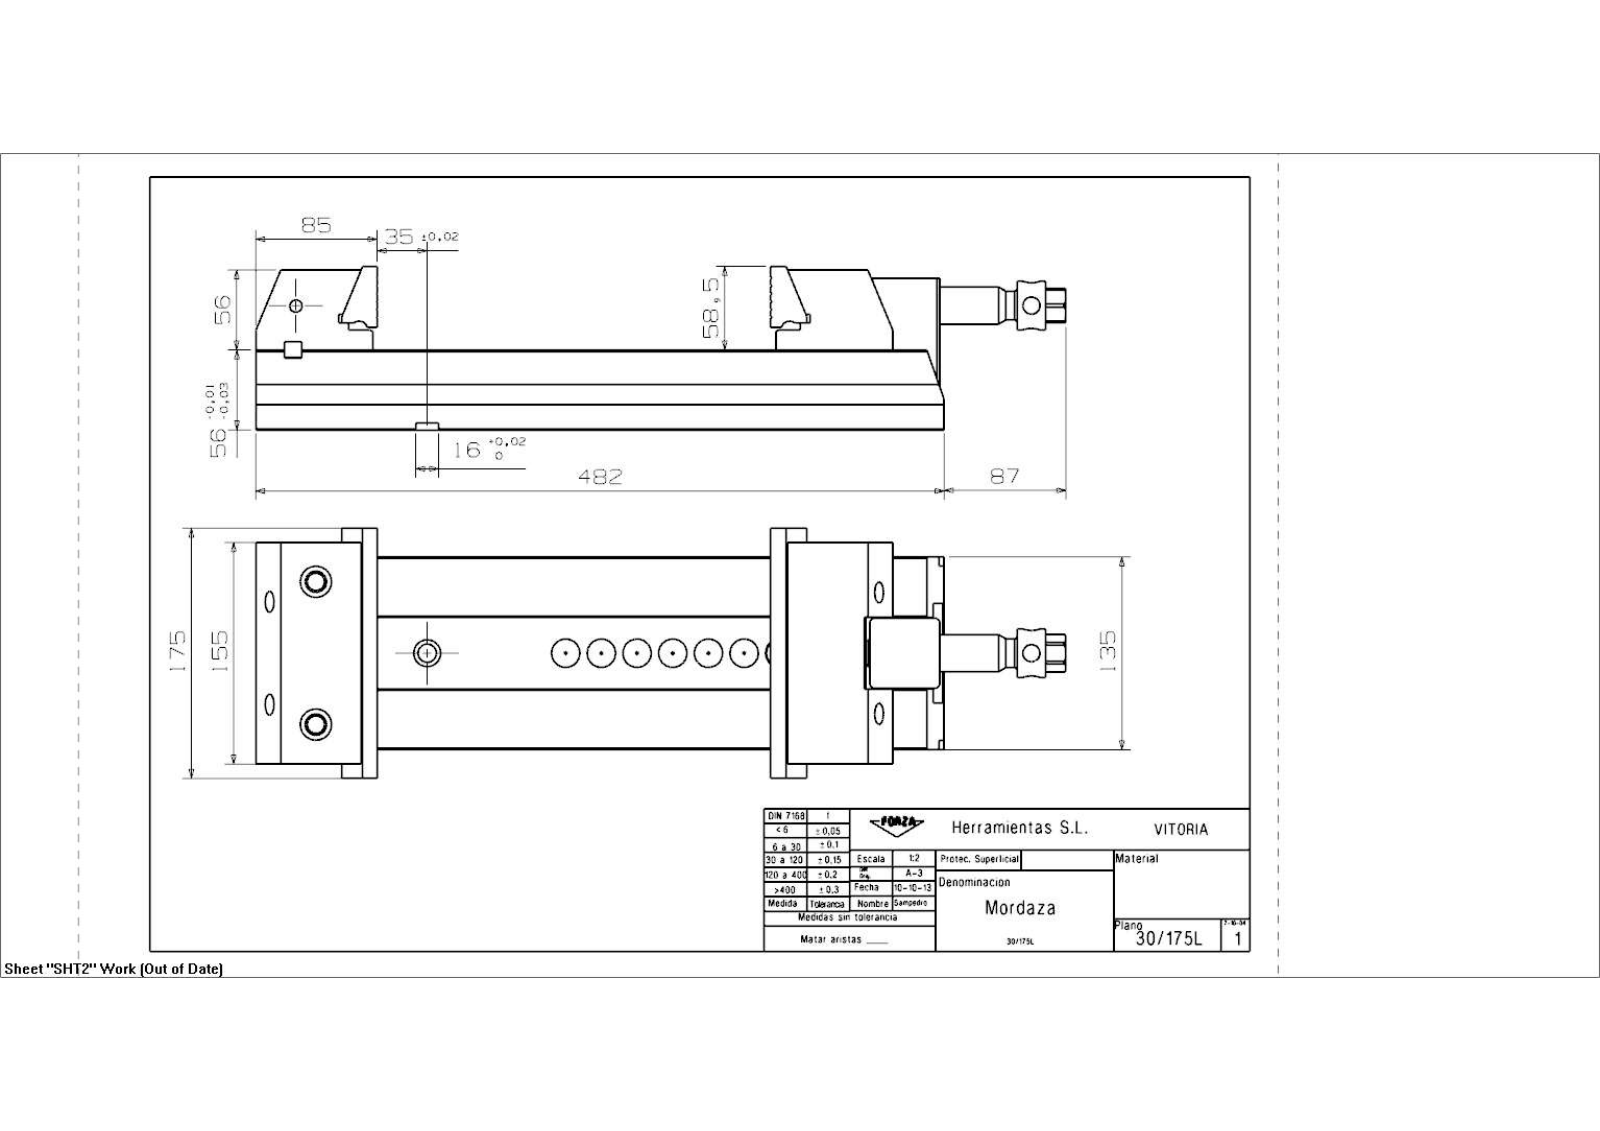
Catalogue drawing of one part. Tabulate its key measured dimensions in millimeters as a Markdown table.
| quantity | value |
| --- | --- |
| part name | 30_175L_Mordaza |
| STEP written by | SIEMENS PLM Software NX 7.5 (CONFIG_CONTROL_DESIGN) |
| units | millimeters |
| bodies | 12 solids, 461 faces (301 planar, 97 cylindrical, 63 other) |
| overall size | 567.23 × 175 × 114.5 |
| volume | 4 084 000 mm³ |
| surface area | 518 025 mm² |
| round holes (diameter × count) | 13 × 6, 15 × 6, 19 × 6, 5.19 × 5, 10 × 4, 10.58 × 4, 8.78 × 3, 6.99 × 2, 8.5 × 2, 12 × 2, 12.38 × 2, 20 × 2 |
| round bosses / shafts (diameter × count) | 34 × 1, 33.8 × 1, 26 × 1, 20 × 1, 16.5 × 1 |
| partial cylindrical surfaces (radius × count) | 8 × 4, 20 × 4, 1.6 × 2, 6 × 2, 7 × 2, 4 × 1, 9 × 1, 10.5 × 1 |
| main face-to-face distances | 56, 31.8, 24.2, 102.5, 10, 42.5, 135, 32.5, 112.5, 112.03 |
| hole center spacings | 6.5, 72, 78.5, 106.07, 100, 27.76, 30, 30.3 |
